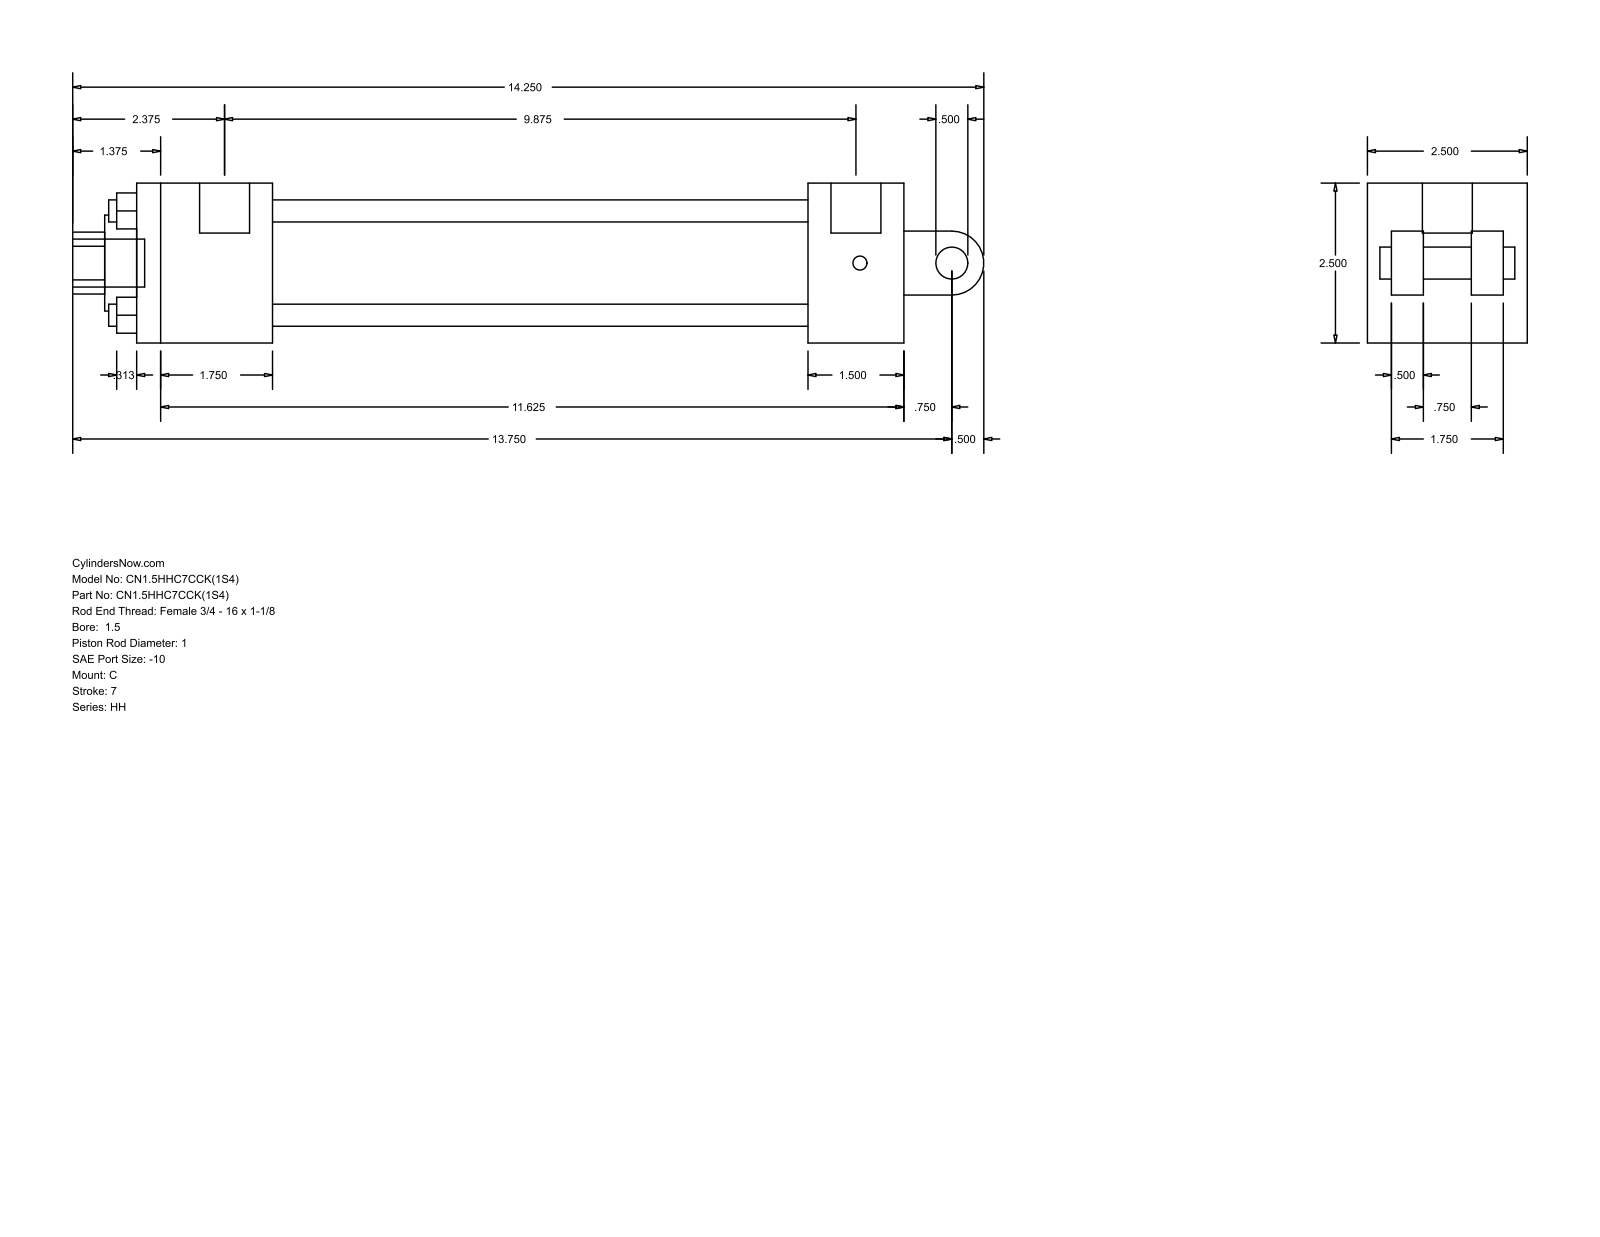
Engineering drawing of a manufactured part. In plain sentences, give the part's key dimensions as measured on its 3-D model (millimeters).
The part is named "HH_C__0150_1". Its 3-D file was written by "GSSL Pune (CONFIG_CONTROL_DESIGN)". It is 0 solids with 99 faces: 70 planar, 29 cylindrical and 0 other. Overall it measures 361.95 by 63.5 by 63.5 millimeters. Round holes: 4 of diameter 8.76, 2 of diameter 5.56, 1 of diameter 19.84, 1 of diameter 25.4, 1 of diameter 38.1, 1 of diameter 44.45. Round bosses or shafts: 2 of diameter 5.56, 1 of diameter 19.84, 1 of diameter 19.05, 1 of diameter 12.7. Partial cylindrical surfaces (rounded edges, fillets, slot ends): 1 of radius 12.29, 1 of radius 12.7. The main face-to-face distances are 63.5, 53.98, 212.72, 250.82, 38.1, 266.7, 304.8, 12.7, 22.22, 41.28. The hole center spacings are 29.27, 41.4, 58.55, 1.59.
